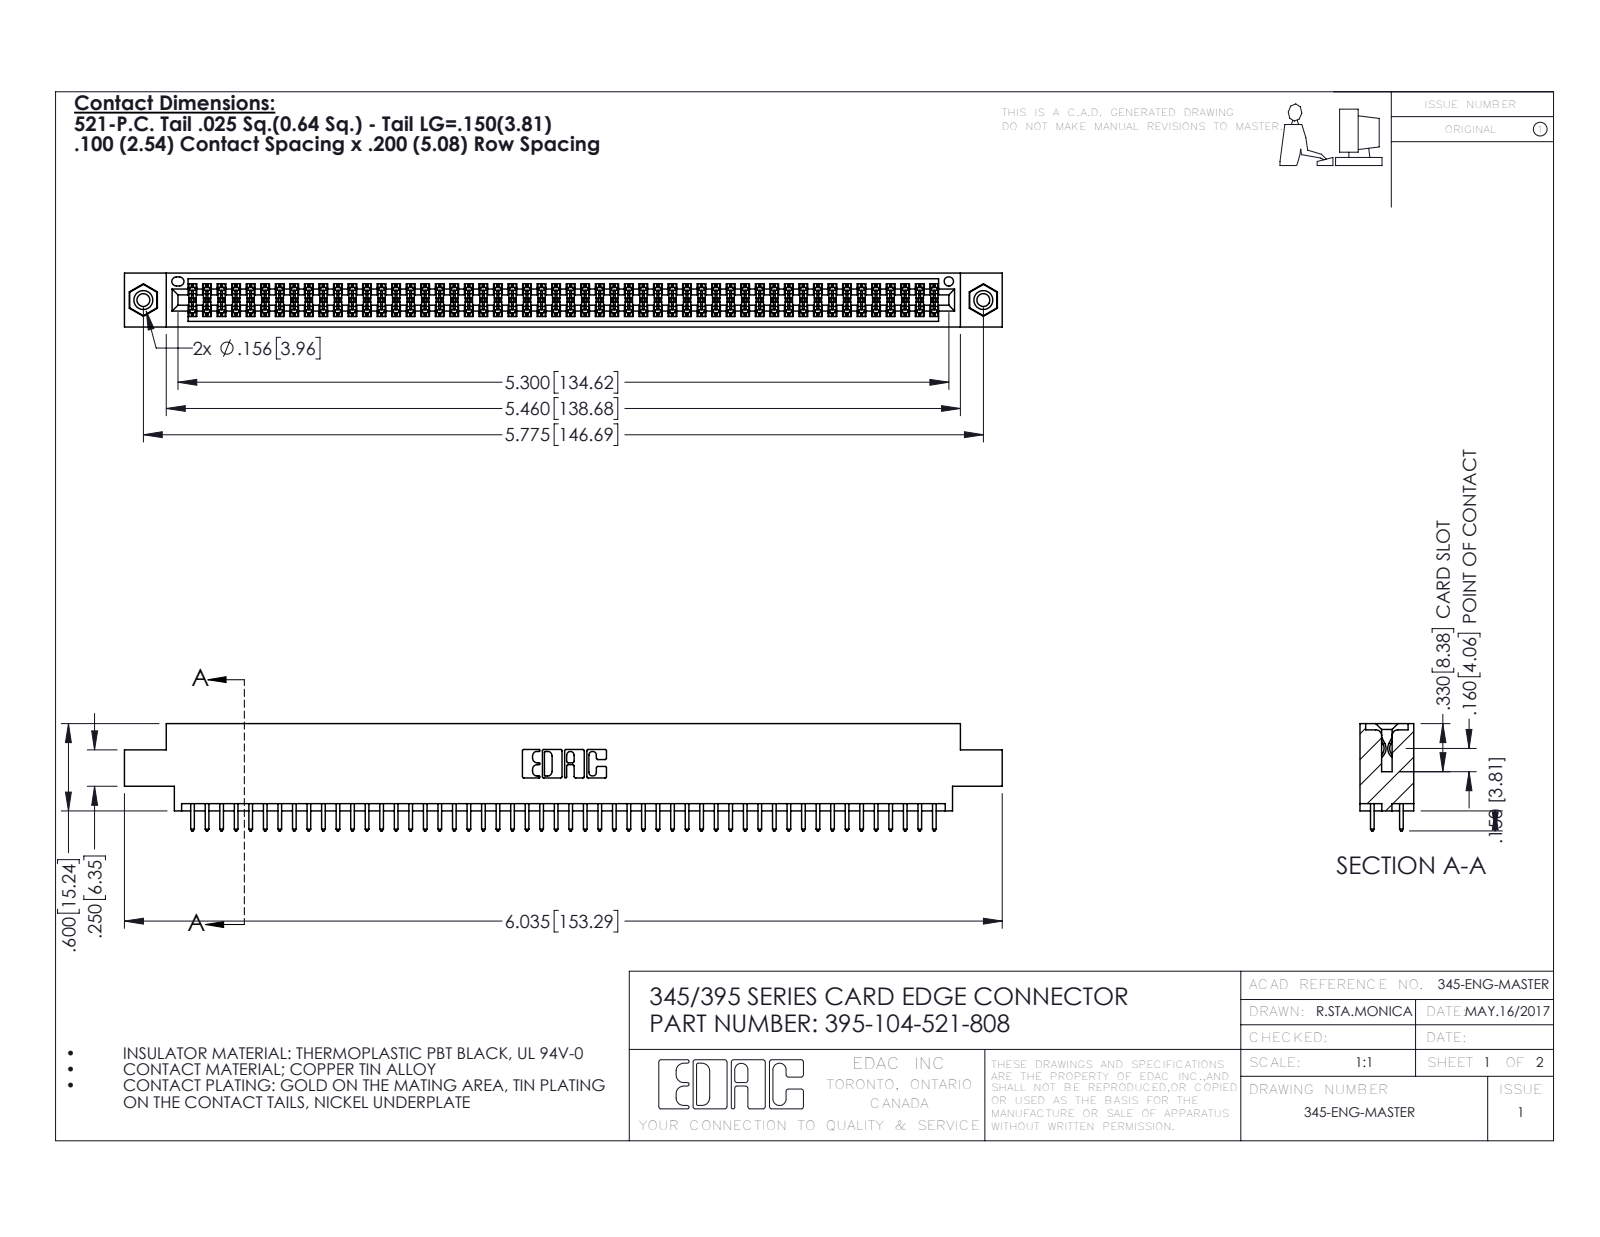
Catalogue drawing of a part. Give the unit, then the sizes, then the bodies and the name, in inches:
Units: inches
Overall size (bounding box): 6.035 × 0.737 × 0.37
Round holes (diameter × count): ⌀0.089 ×2, ⌀0.125 ×2, ⌀0.156 ×2, ⌀0.064 ×1
Round bosses / shafts (diameter × count): ⌀0.155 ×2
Partial cylindrical surfaces — rounded edges, fillets, slot ends (radius × count): R0.006 ×156, R0.01 ×104, R0.01 ×22, R0.007 ×6, R0.031 ×6, R0.026 ×3, R0.014 ×2, R0.019 ×2
Main face-to-face distances: 0.072, 0.298, 0.2, 0.37, 0.098, 0.272, 0.025, 0.225, 0.175, 0.149
Hole centre spacings: 0.27, 5.539, 5.775
Volume: 0.904 in³ · Surface area: 34.07 in²
Bodies: 107 solids, 5390 faces (3548 planar, 1826 cylindrical, 16 other)
Part name (STEP PRODUCT): 345 Part_0.170 Offset - 0.156 Dia-TI; 345-292-001_345-293-121; 345-250-001_345-250-003-102; 395-104-521-808
STEP written by: SolidWorks 2016 (CONFIG_CONTROL_DESIGN)
